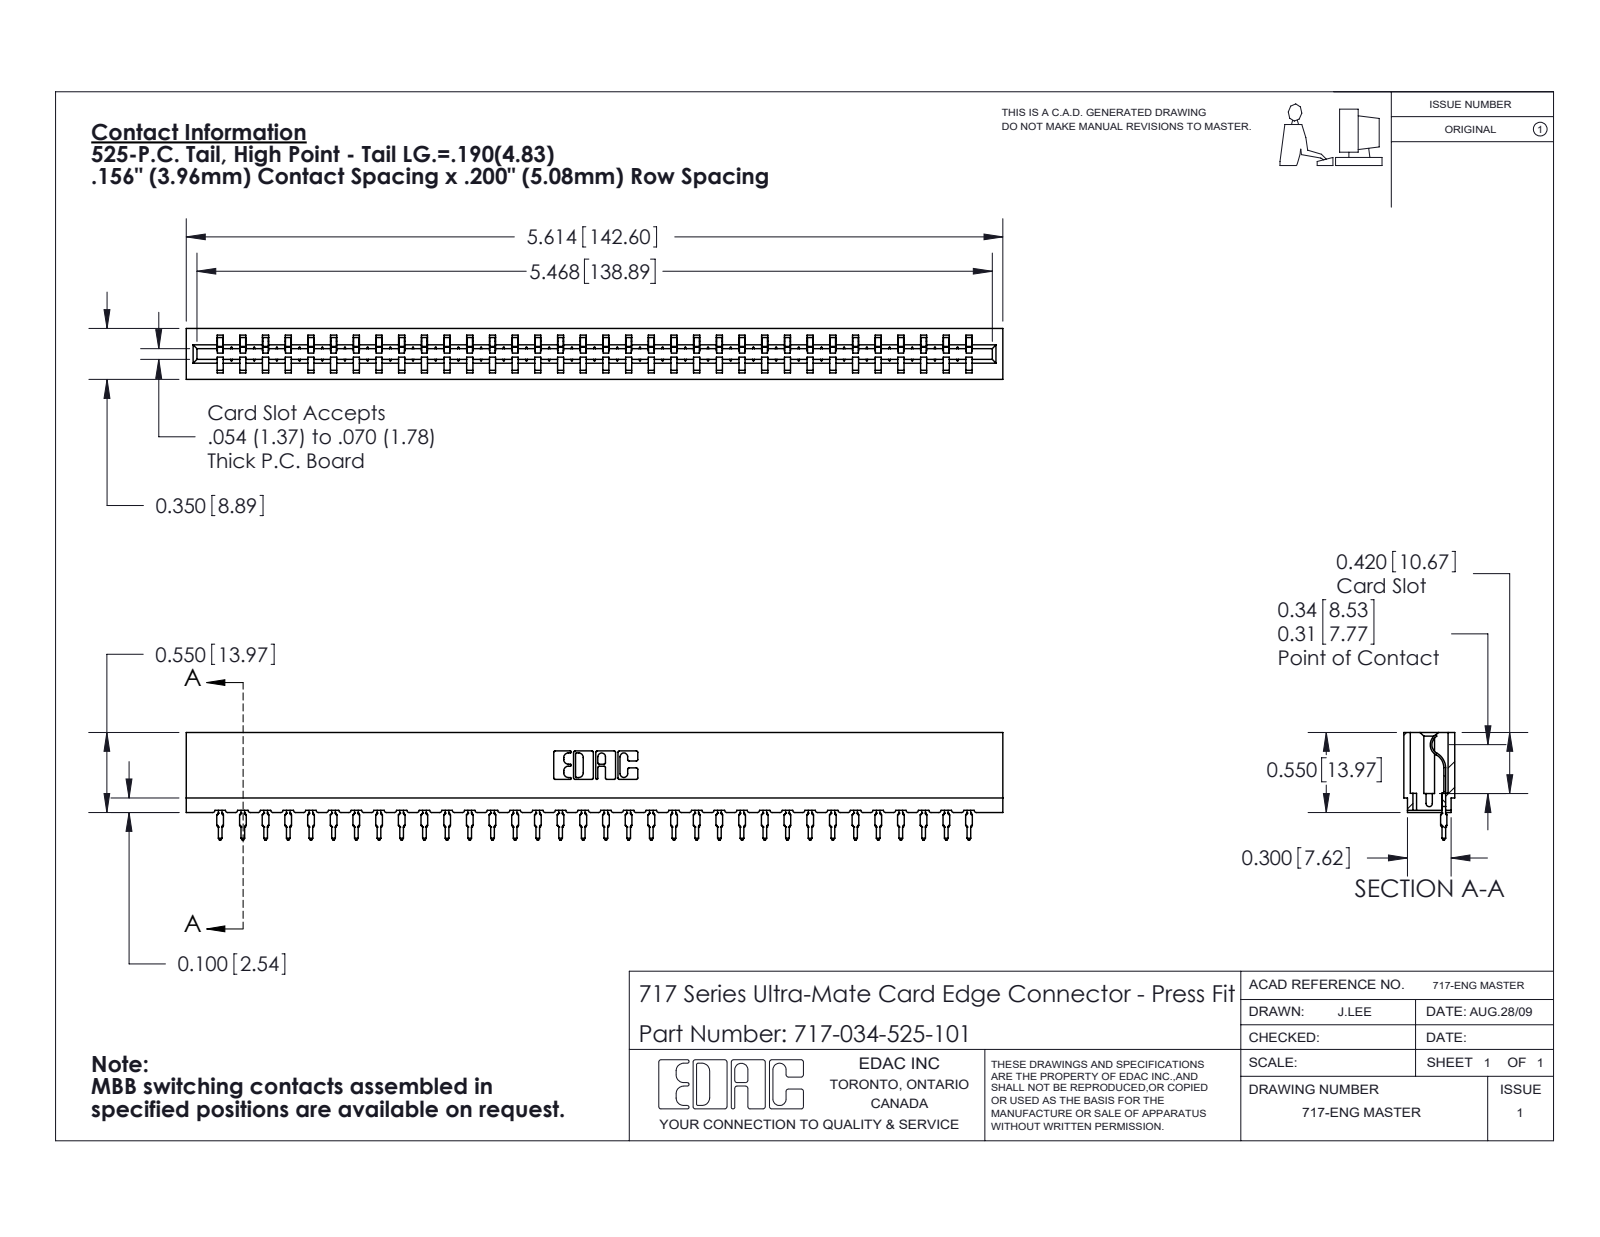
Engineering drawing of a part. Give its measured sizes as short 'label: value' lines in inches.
name: 717 Part_Insulator Option - 06; 717-034-525-101; 745-292-001_525
written by: SolidWorks 2020 (CONFIG_CONTROL_DESIGN)
unit: in
bodies: 35 solids, 3936 faces (2366 planar, 686 cylindrical, 884 other)
size: 5.614 × 0.739 × 0.35
volume: 0.735 in³; area: 25.94 in²
rounds: 68× R0.015, 68× R0.021, 22× R0.01, 6× R0.007, 6× R0.031, 4× R0.005, 4× R0.011, 3× R0.026
face distances: 0.212, 0.138, 0.35, 0.074, 0.156, 0.045, 0.305, 0.093, 0.167, 0.025
